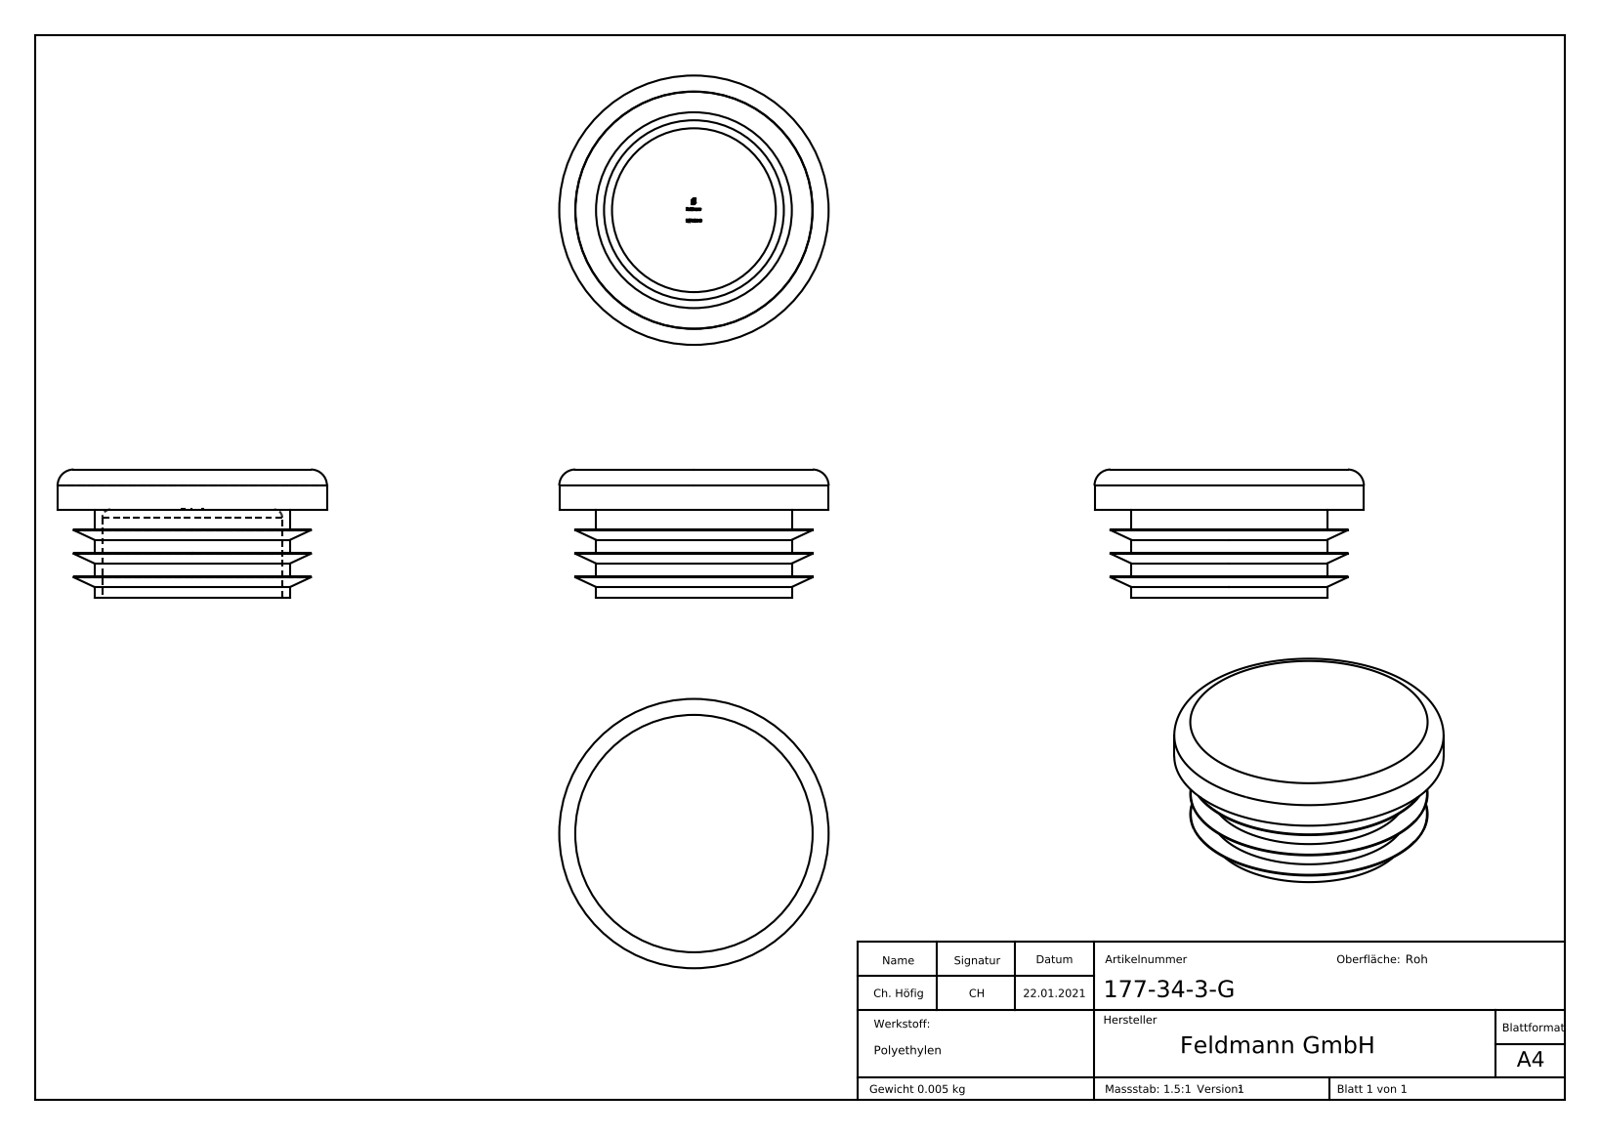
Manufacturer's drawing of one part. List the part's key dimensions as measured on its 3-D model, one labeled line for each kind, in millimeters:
Part name (STEP PRODUCT): 177-34-3-G
STEP written by: SolidWorks 2018 (CONFIG_CONTROL_DESIGN)
Units: millimetres
Bodies: 1 solid, 290 faces (157 planar, 12 cylindrical, 121 other)
Overall size (bounding box): 33.7 × 33.7 × 16
Volume: 5 644 mm³ · Surface area: 4 929 mm²
Round holes (diameter × count): ⌀22.5 ×1
Round bosses / shafts (diameter × count): ⌀33.7 ×1, ⌀24.5 ×1
Main face-to-face distances: 5, 2.95, 5.45, 10.45, 8.4, 13.4, 5.9, 2.5, 7.5, 2.6
